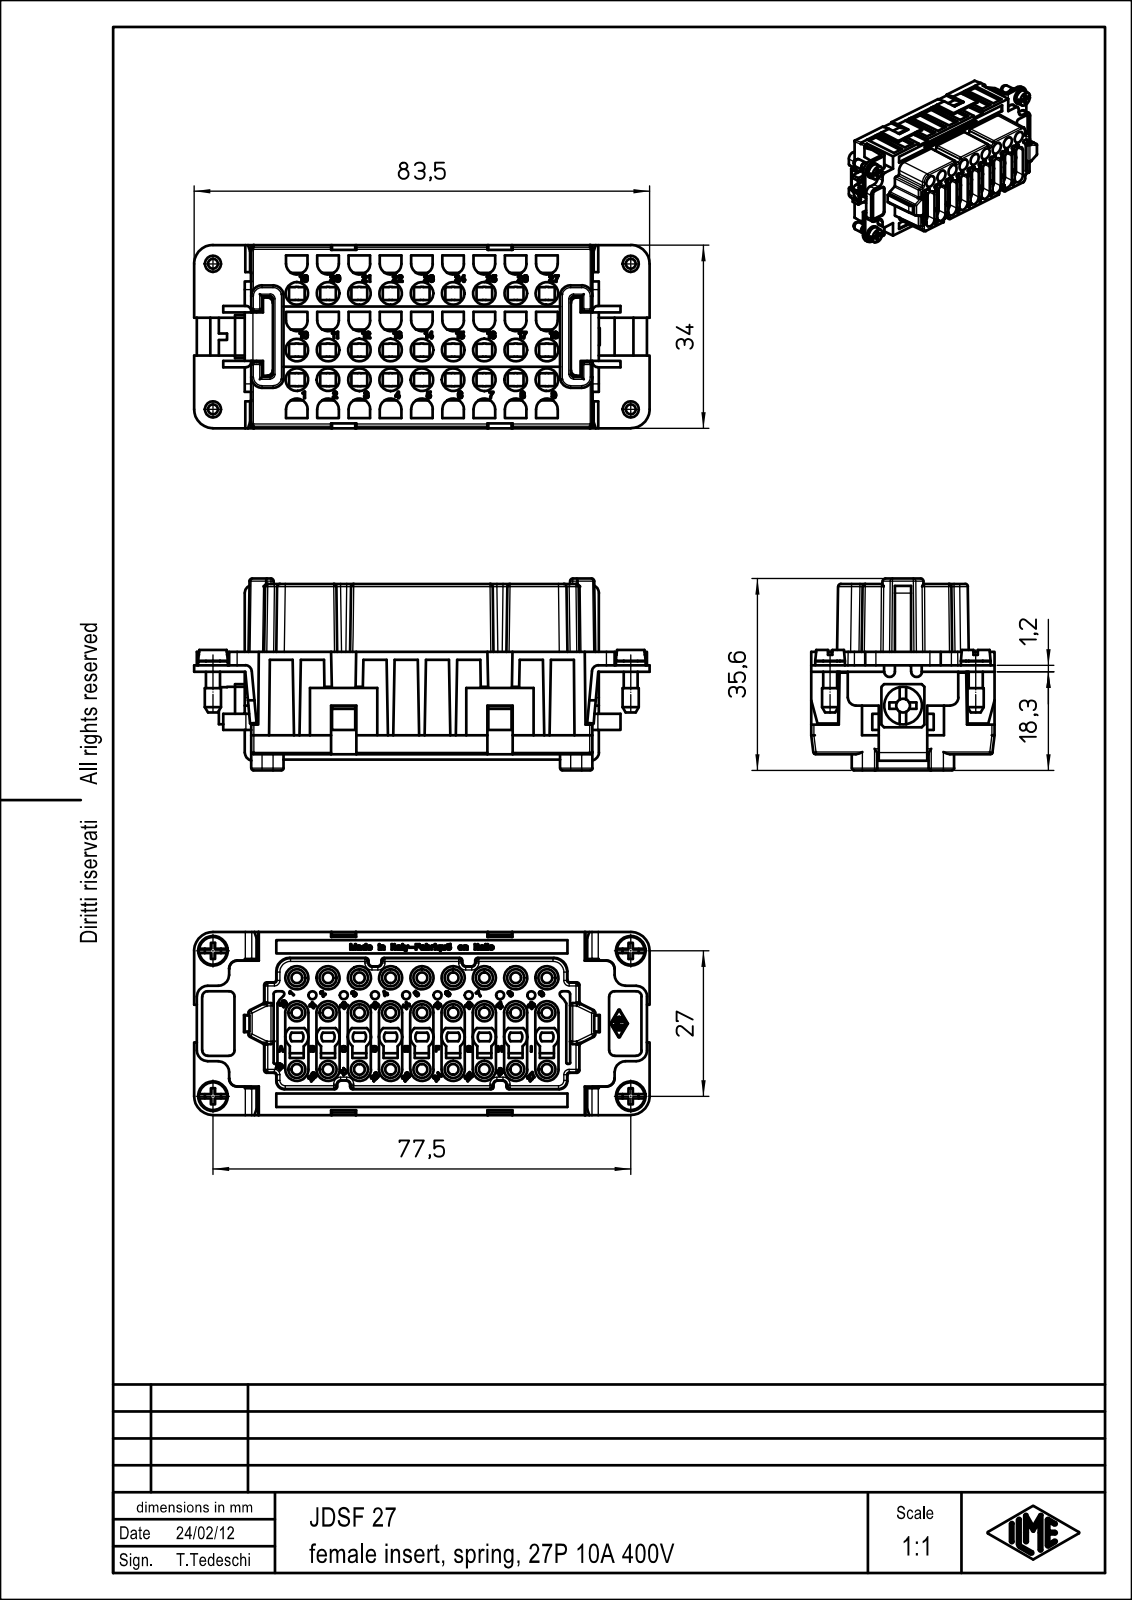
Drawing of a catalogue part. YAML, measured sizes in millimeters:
part_name: "JDSF_27"
step_written_by: "Creo Elements/Direct Modeling 18.0B 02-Dec-2011 (C) Parametric Technology GmbH (AUTOMOTIVE_DESIGN)"
units: millimeters
bodies: {solids: 1, faces: 6562, planar: 5854, cylindrical: 467, other: 241}
overall_size: [84.5, 35.6, 34]
volume: 53083
surface_area: 23625
round_holes:
  - {diameter: 2, count: 27}
  - {diameter: 4.2, count: 27}
  - {diameter: 4.3, count: 9}
  - {diameter: 1.5, count: 8}
  - {diameter: 2.58, count: 1}
  - {diameter: 3, count: 1}
round_bosses_or_shafts:
  - {diameter: 5.5, count: 4}
  - {diameter: 3, count: 4}
  - {diameter: 2.6, count: 4}
  - {diameter: 7, count: 1}
partial_cylinders:
  - {radius: 0.5, count: 61}
  - {radius: 2, count: 43}
  - {radius: 2.15, count: 27}
  - {radius: 1, count: 20}
  - {radius: 0.4, count: 18}
  - {radius: 1.5, count: 14}
  - {radius: 1.25, count: 9}
  - {radius: 0.8, count: 8}
face_to_face_distances: [1.2, 0.9, 33.1, 1, 16.3, 19, 18.7, 11.5, 2.2, 11.6]
hole_center_spacings: [4.36, 5.8, 11.6, 9.29, 17.4, 12, 14.05, 23.2]
